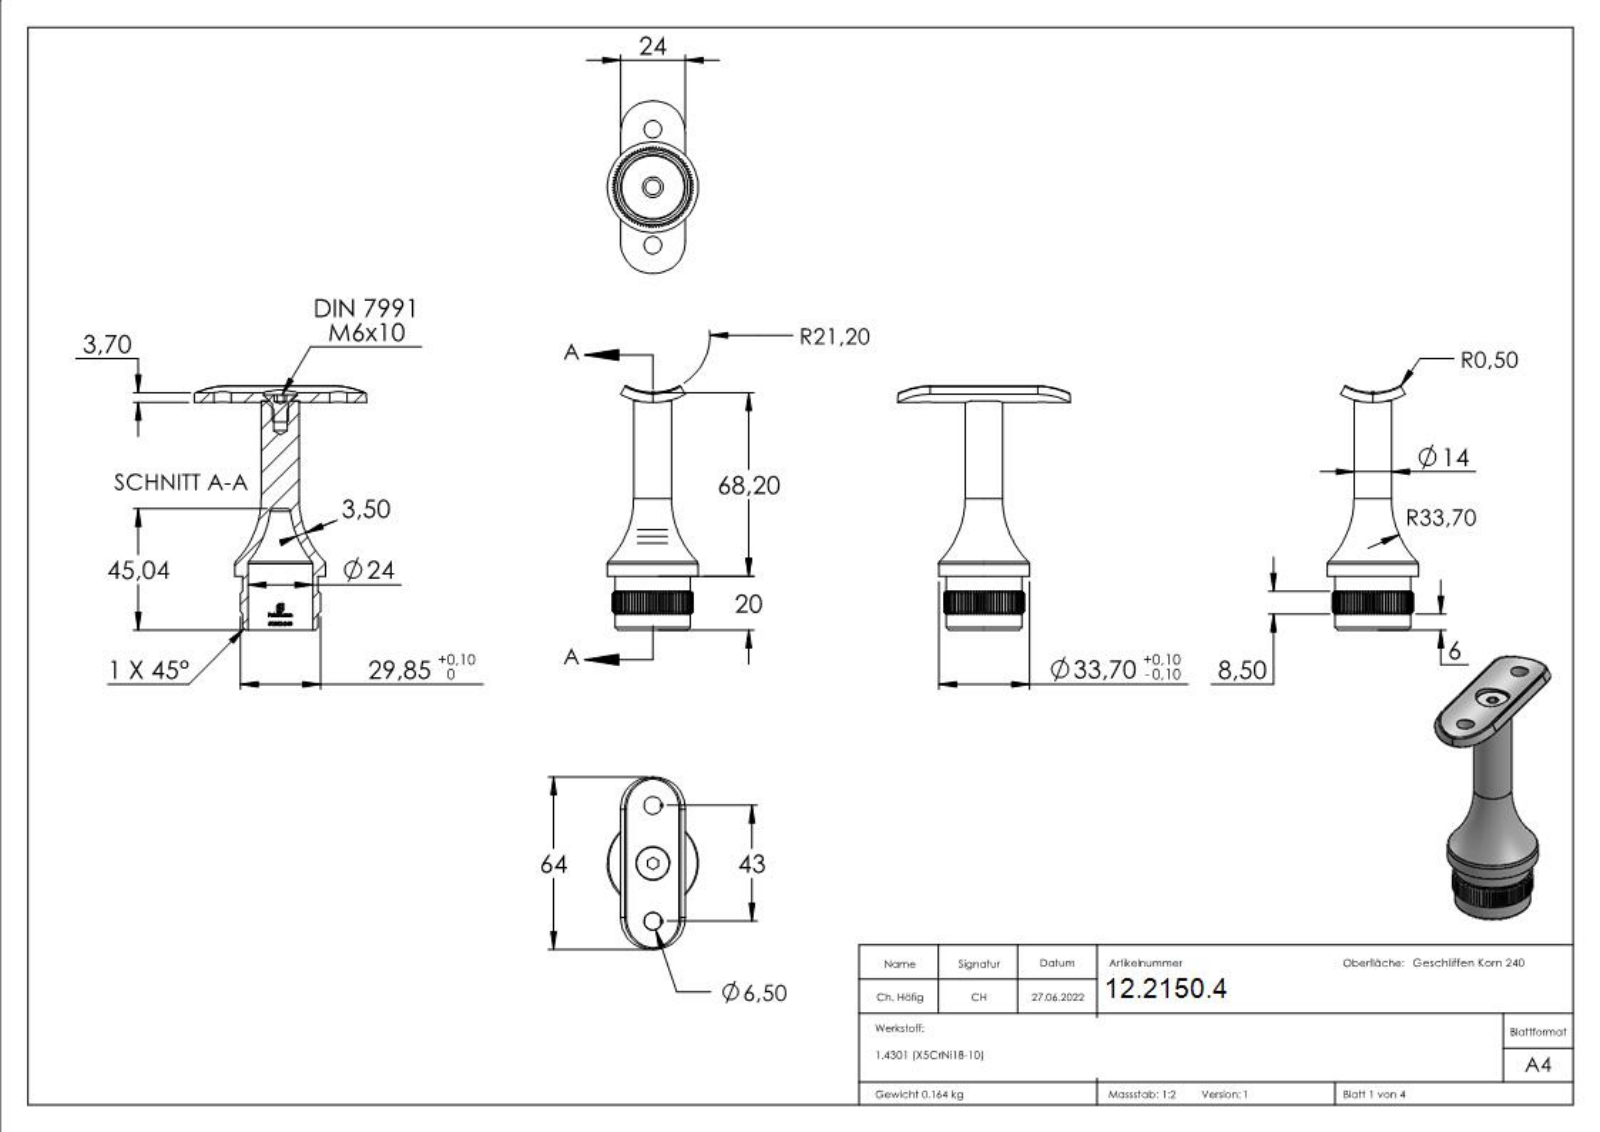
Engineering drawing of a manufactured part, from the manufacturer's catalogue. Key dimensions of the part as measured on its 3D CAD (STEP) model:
Part name (STEP PRODUCT): DIN 7991 Konfig_DIN 7991 M6x10; 5025x-240 Teil1_50252-240 Teil1; 50252-240; 5025x-240 Teil2_5025x-240 Teil2
STEP written by: SolidWorks 2018 (CONFIG_CONTROL_DESIGN)
Units: millimetres
Bodies: 3 solids, 724 faces (298 planar, 130 cylindrical, 296 other)
Overall size (bounding box): 90.65 × 64 × 33.7
Volume: 20 762 mm³ · Surface area: 13 593 mm²
Round holes (diameter × count): ⌀6.5 ×2, ⌀5 ×1, ⌀8.1 ×1, ⌀12.5 ×1, ⌀24 ×1
Round bosses / shafts (diameter × count): ⌀33.7 ×1, ⌀28 ×1, ⌀14 ×1, ⌀12 ×1, ⌀6 ×1
Partial cylindrical surfaces — rounded edges, fillets, slot ends (radius × count): R12 ×4, R0.5 ×2, R7.1 ×1, R12.1 ×1, R14.93 ×1, R21.2 ×1, R24.9 ×1
Main face-to-face distances: 14, 14.02, 65, 13.98, 67.35, 2.35, 20, 85, 87.35, 45.04
Hole centre spacings: 21.5, 43
